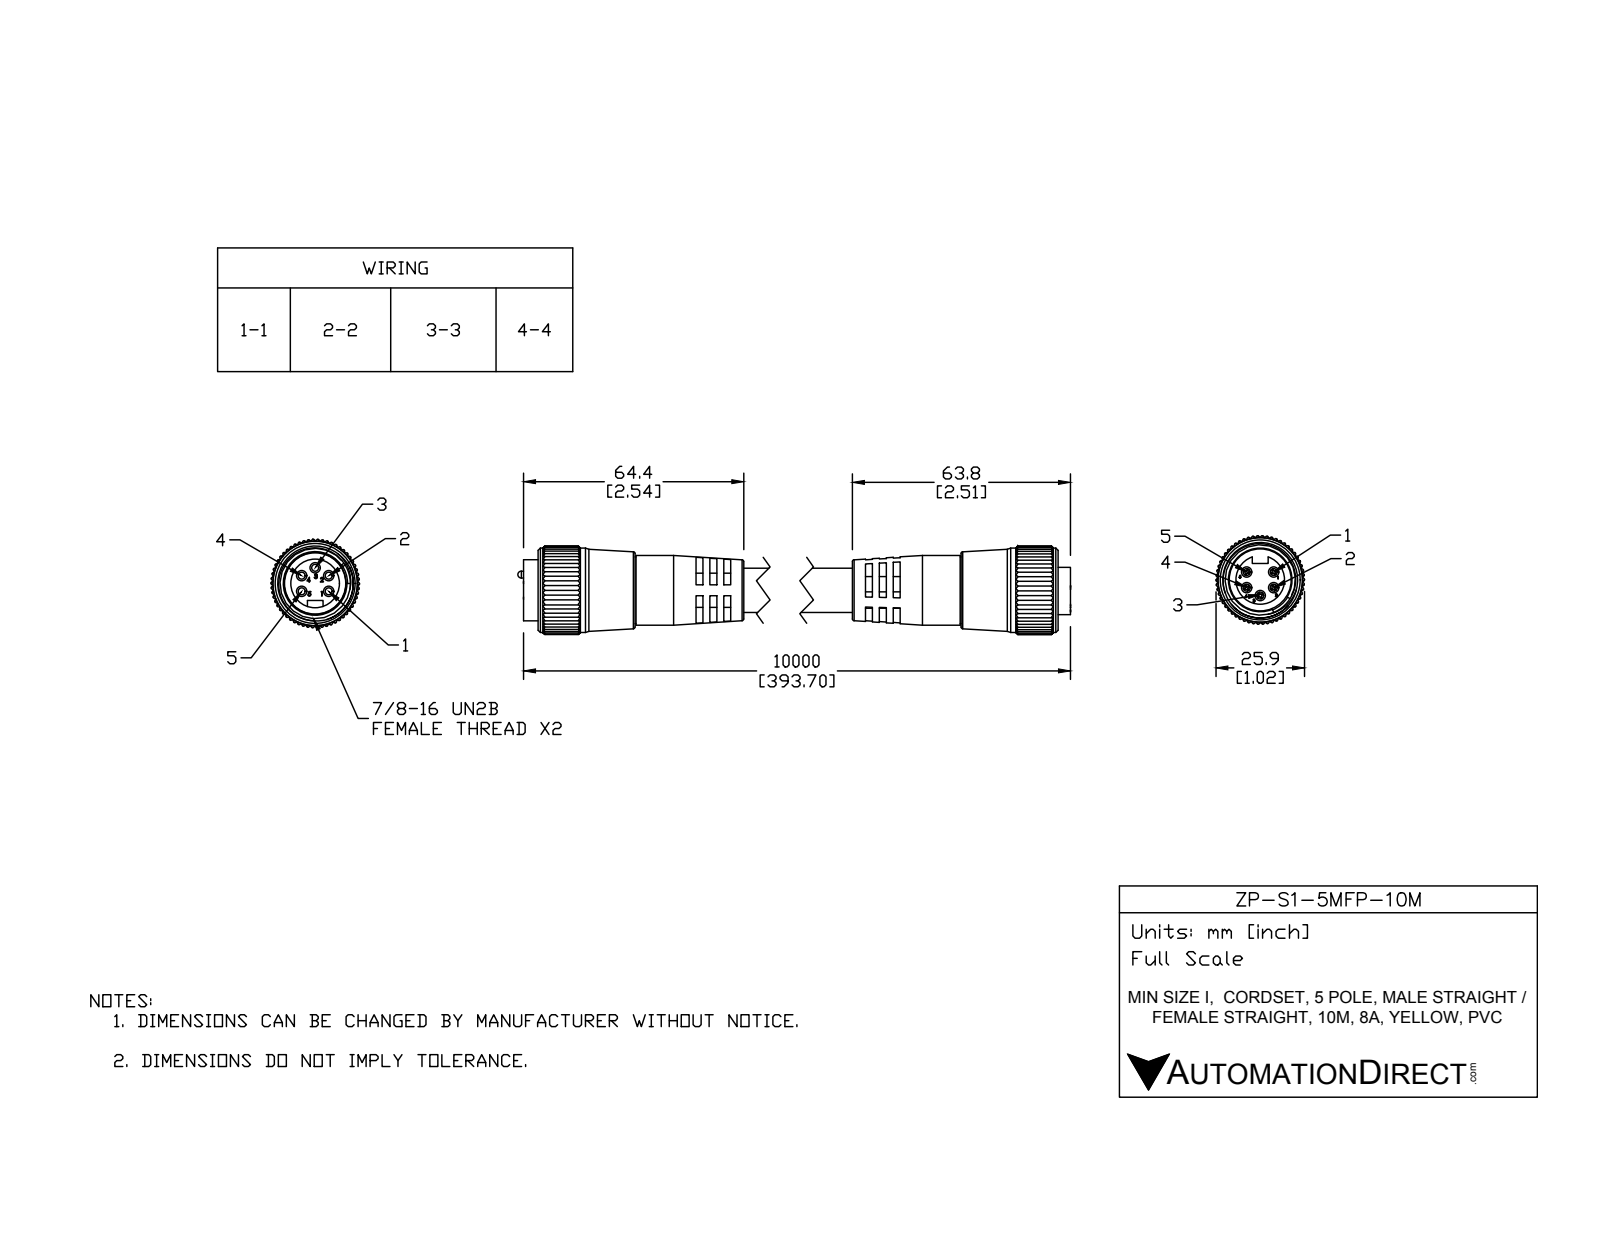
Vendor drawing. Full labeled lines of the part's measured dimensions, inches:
Part name (STEP PRODUCT): ZP-S1-5MFP-10M
STEP written by: SolidWorks 2015 (AUTOMOTIVE_DESIGN)
Units: inches
Bodies: 9 solids, 1185 faces (439 planar, 630 cylindrical, 116 other)
Overall size (bounding box): 9.042 × 1.017 × 1.017
Volume: 3.103 in³ · Surface area: 36.34 in²
Round holes (diameter × count): ⌀0.12 ×5, ⌀0.786 ×1, ⌀0.805 ×1, ⌀0.827 ×1
Round bosses / shafts (diameter × count): ⌀0.079 ×5, ⌀0.972 ×1, ⌀0.803 ×1, ⌀0.768 ×1, ⌀0.704 ×1, ⌀0.56 ×1, ⌀0.39 ×1, ⌀0.12 ×1
Partial cylindrical surfaces — rounded edges, fillets, slot ends (radius × count): R0.01 ×165, R0.09 ×1, R0.207 ×1, R0.509 ×1
Main face-to-face distances: 0.079, 0.158, 4.633, 4.474, 0.159, 4.95, 2.356, 0.159, 4.791, 4.792
Hole centre spacings: 0.18, 0.18, 0.311, 0.312, 0.36
